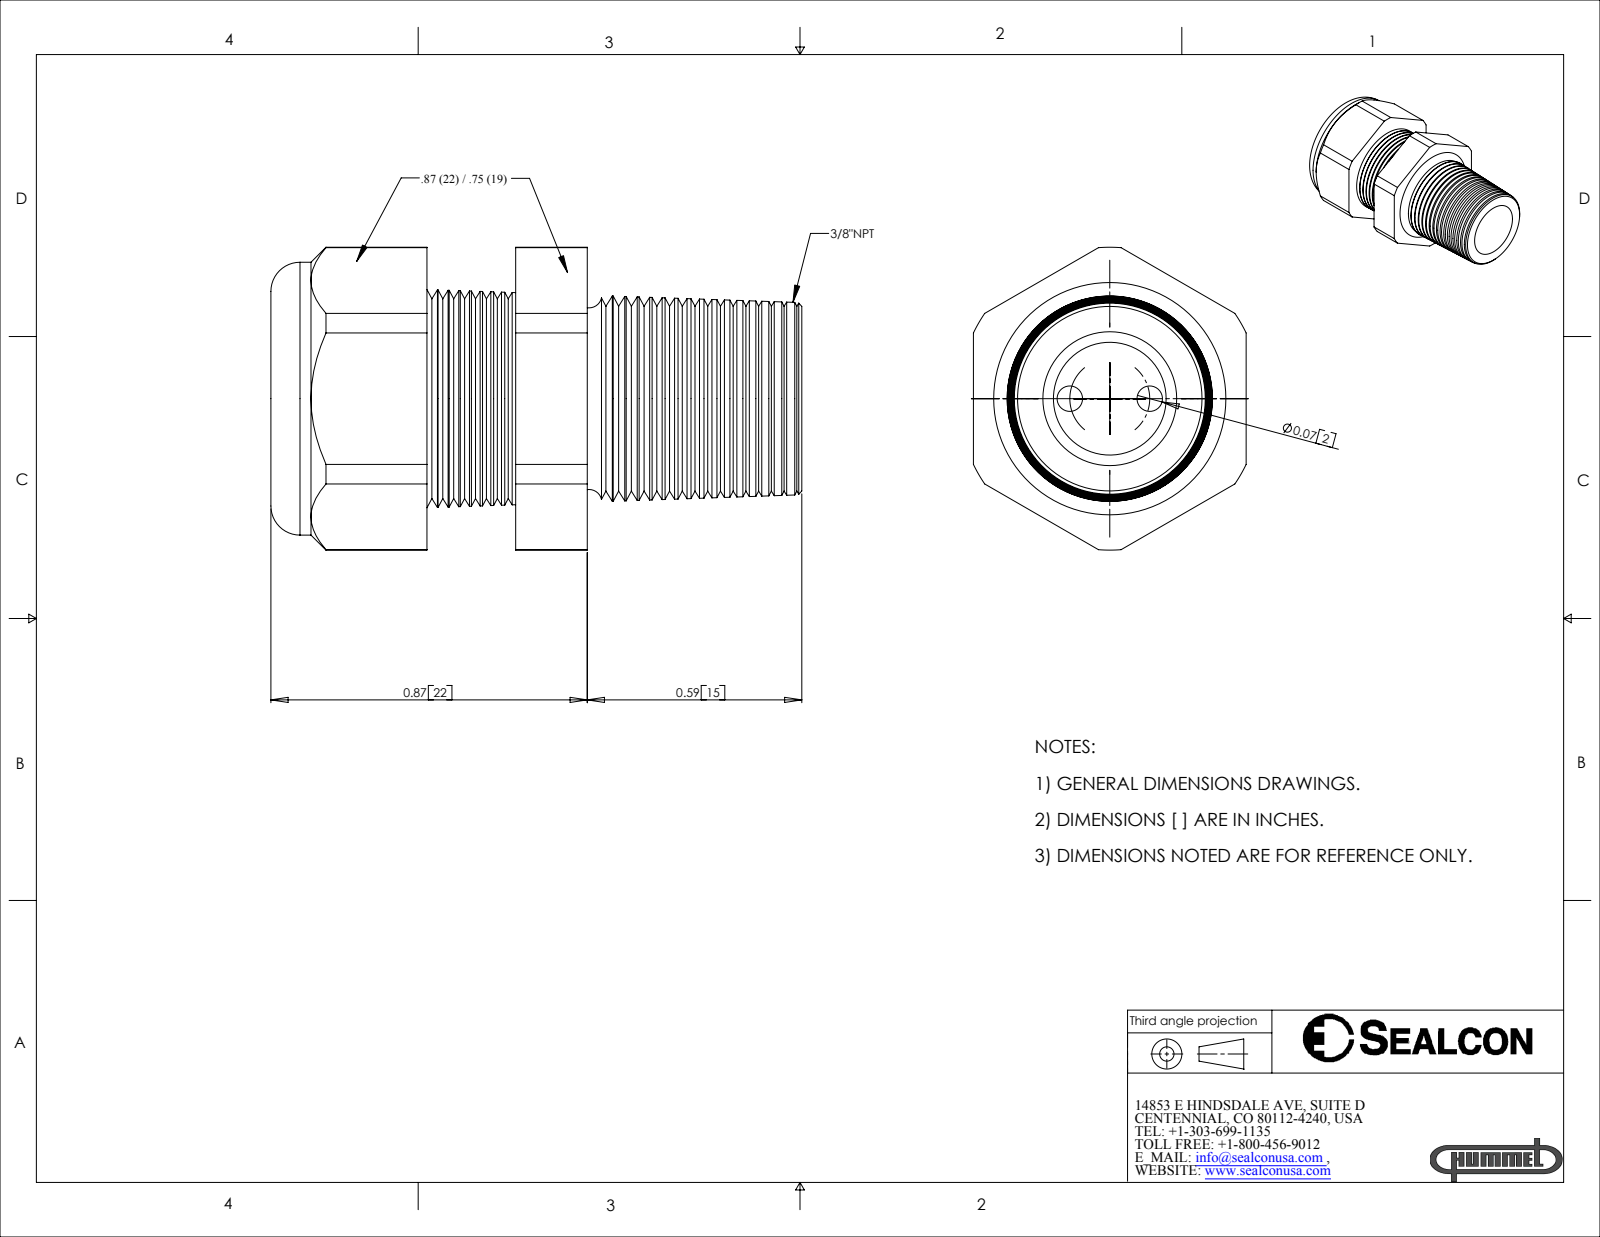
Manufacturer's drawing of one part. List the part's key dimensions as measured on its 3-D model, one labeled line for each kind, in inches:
Part name (STEP PRODUCT): CD09N4-GY
STEP written by: SolidWorks 2007 (CONFIG_CONTROL_DESIGN)
Units: inches
Bodies: 2 solids, 202 faces (20 planar, 24 cylindrical, 158 other)
Overall size (bounding box): 1.46 × 0.833 × 0.75
Volume: 0.369 in³ · Surface area: 6.999 in²
Round holes (diameter × count): ⌀0.07 ×2, ⌀0.29 ×1, ⌀0.31 ×1
Round bosses / shafts (diameter × count): ⌀0.75 ×1
Partial cylindrical surfaces — rounded edges, fillets, slot ends (radius × count): R0.416 ×1
Main face-to-face distances: 0.75, 0.673, 0.429, 0.244, 0.75, 0.87, 0.441, 0.197, 1.46, 1.031
Hole centre spacings: 0.11, 0.22
